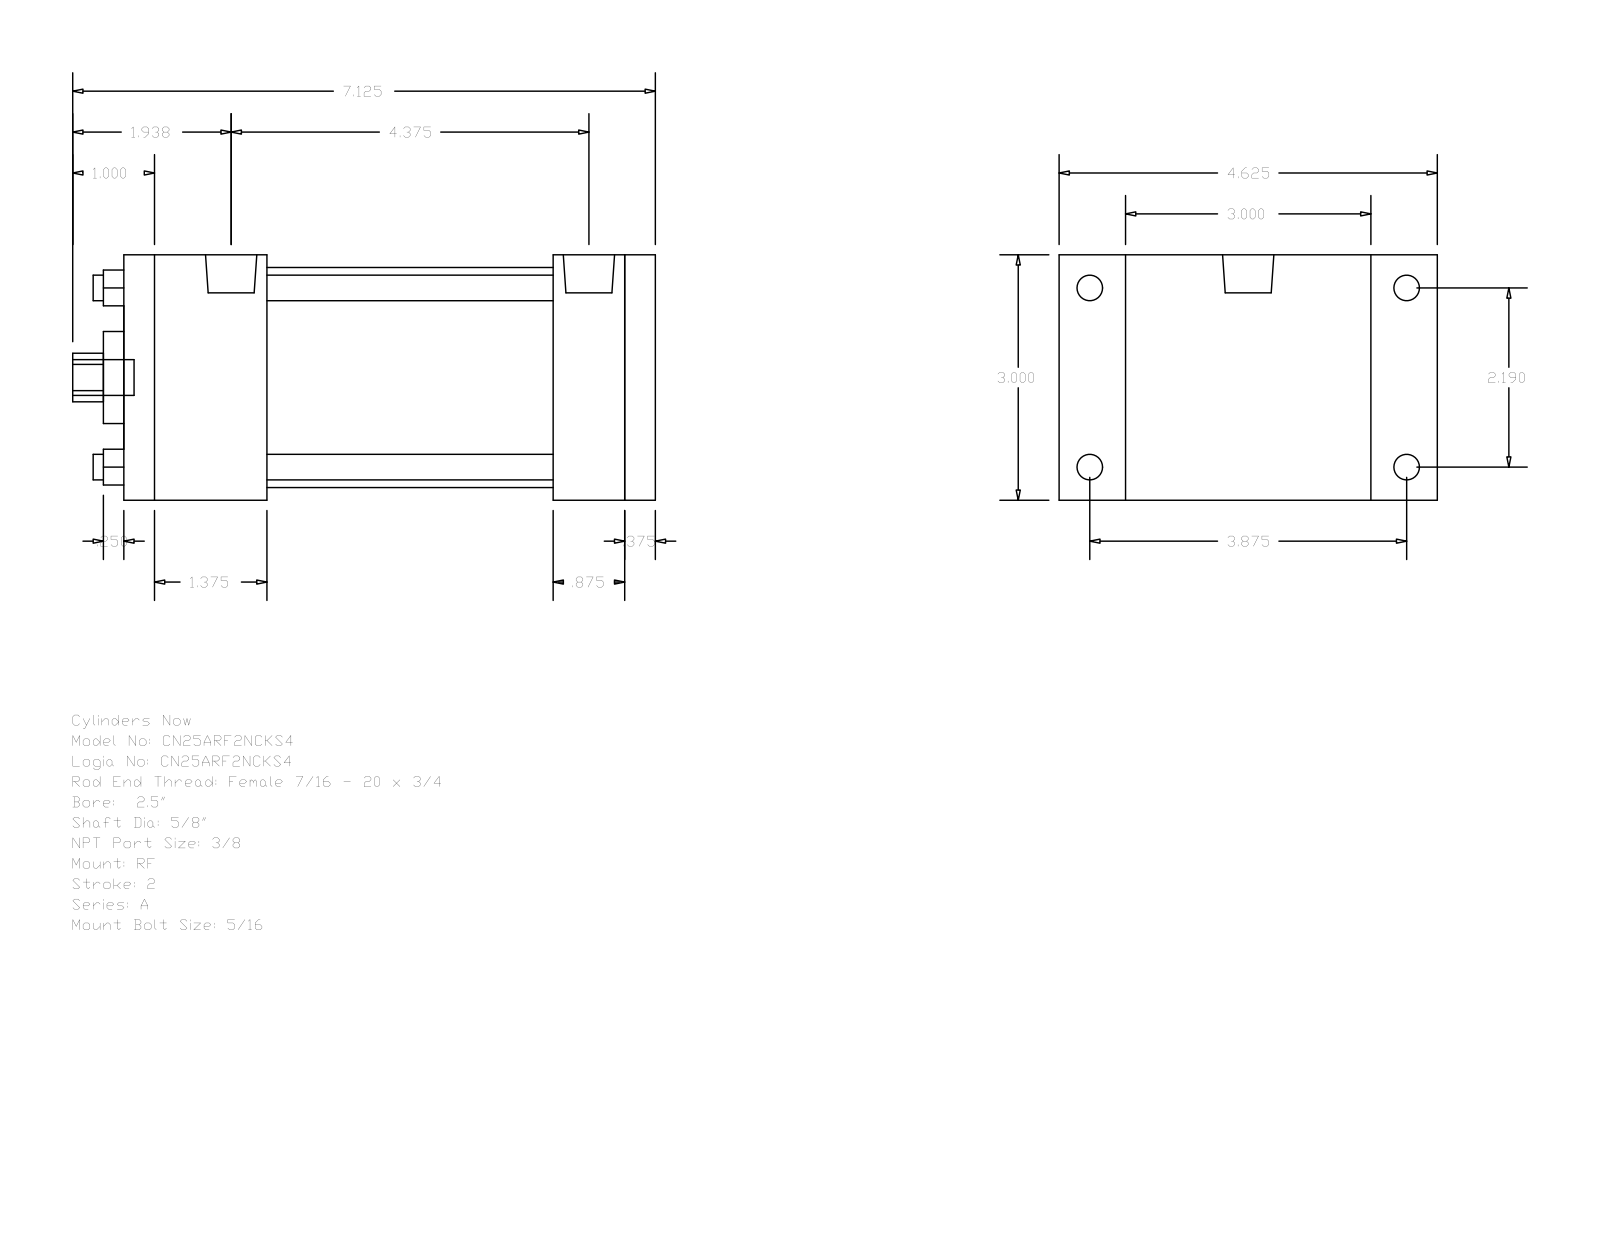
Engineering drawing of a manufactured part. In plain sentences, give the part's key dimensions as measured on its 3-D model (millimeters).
The part is named "A_RF__0250_0.625". Its 3-D file was written by "GSSL Pune (CONFIG_CONTROL_DESIGN)". It is 0 solids with 92 faces: 64 planar, 28 cylindrical and 0 other. Overall it measures 180.97 by 117.47 by 76.2 millimeters. Round holes: 4 of diameter 7.94, 1 of diameter 15.88, 1 of diameter 28.57, 1 of diameter 68.33. Round bosses or shafts: 4 of diameter 7.94, 4 of diameter 5.56, 2 of diameter 15.93, 1 of diameter 11.11. Partial cylindrical surfaces (rounded edges, fillets, slot ends): 1 of radius 7.54. The main face-to-face distances are 76.2, 165.09, 9.52, 155.57, 44.45, 31.75, 133.34, 88.89, 111.12, 120.64. The hole center spacings are 39.33, 55.62, 78.66.
